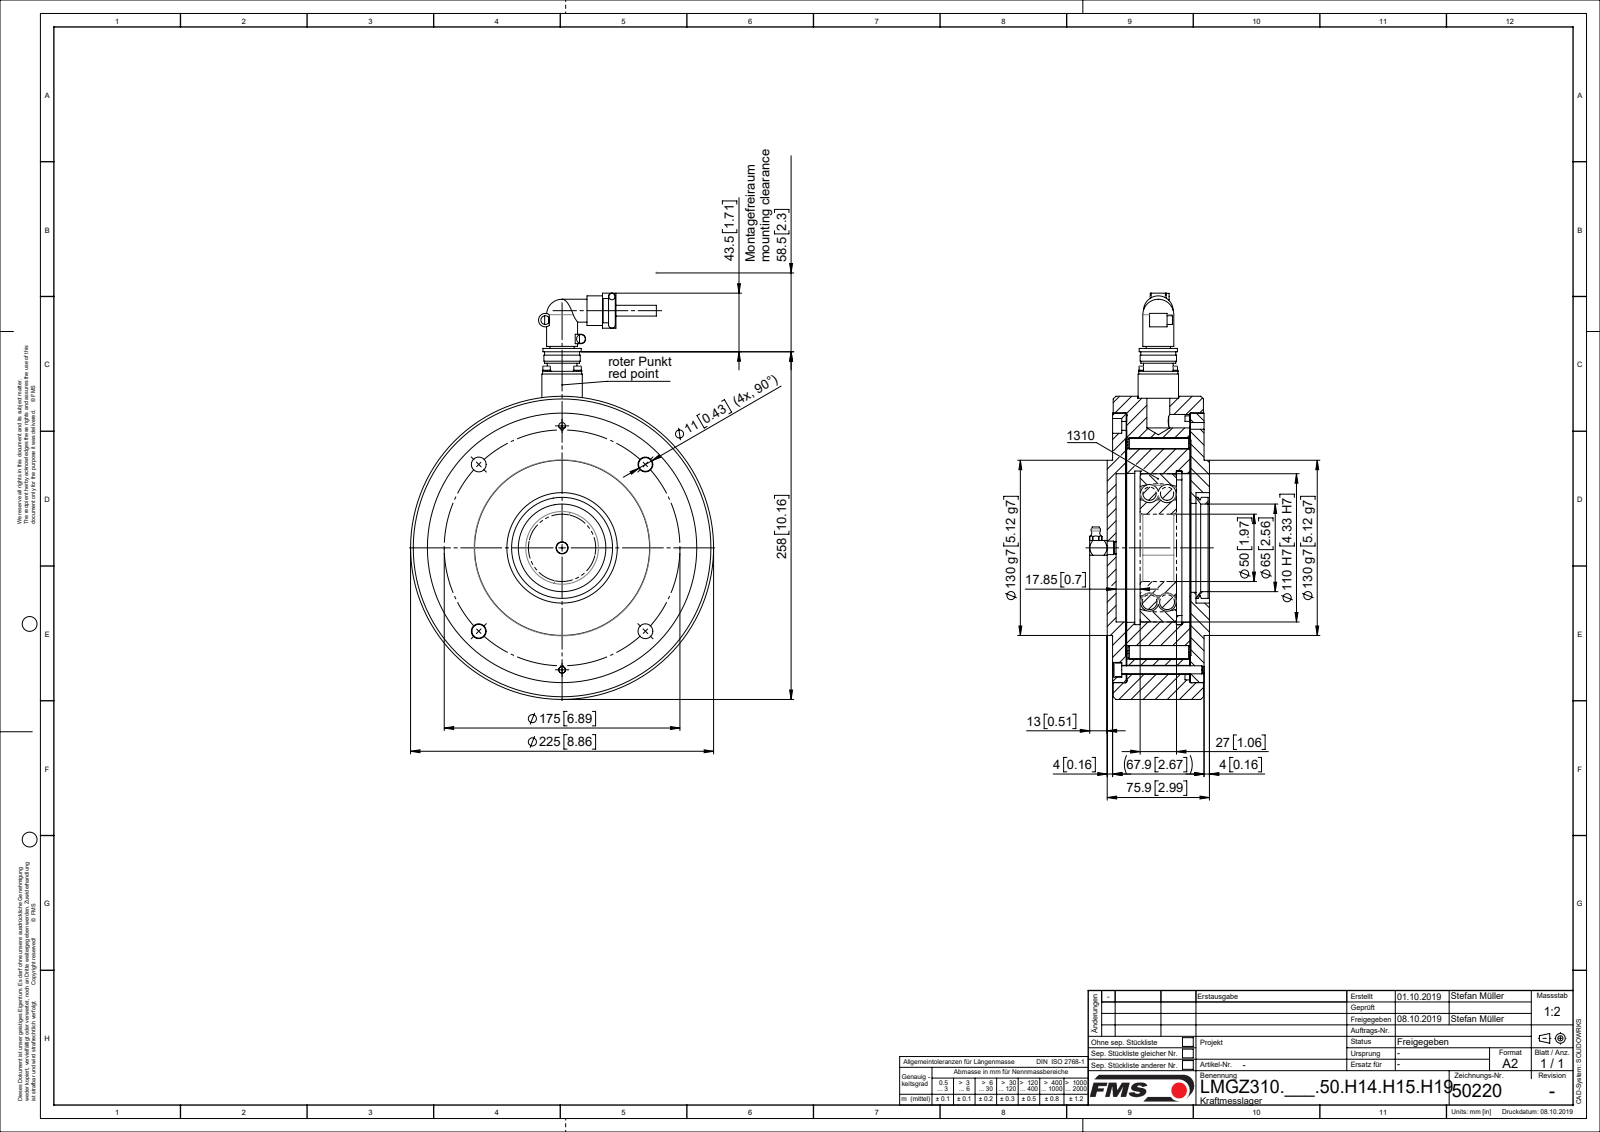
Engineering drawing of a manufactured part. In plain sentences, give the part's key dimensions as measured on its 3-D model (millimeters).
The part is named "L50220; L49380; TEIL1; L49026 (+8 more)". Its 3-D file was written by "Mechanical Desktop 2007 (CONFIG_CONTROL_DESIGN)". It is 20 solids with 417 faces: 128 planar, 230 cylindrical and 59 other. Overall it measures 301.5 by 225 by 126.8 millimeters. Its volume is 2 415 000 cubic millimeters and its surface area 391 796 square millimeters. Round holes: 6 of diameter 11, 4 of diameter 2.6, 4 of diameter 3.2, 4 of diameter 3.4, 4 of diameter 3.5, 4 of diameter 9, 2 of diameter 5, 2 of diameter 6.6, 1 of diameter 8.68, 1 of diameter 23, 1 of diameter 50, 1 of diameter 64. Round bosses or shafts: 4 of diameter 6.2, 4 of diameter 5.5, 4 of diameter 3, 2 of diameter 22, 2 of diameter 10, 2 of diameter 8, 2 of diameter 6.5, 2 of diameter 4.8. Partial cylindrical surfaces (rounded edges, fillets, slot ends): 2 of radius 2.5, 1 of radius 3.5, 1 of radius 5, 1 of radius 81, 1 of radius 86. The main face-to-face distances are 9.7, 47.25, 10.75, 47.45, 10.2, 10.45, 57.45, 57.7, 47, 10. The hole center spacings are 16.26, 23, 87.5, 32.53, 68.17, 68.18, 90.5, 123.74.
